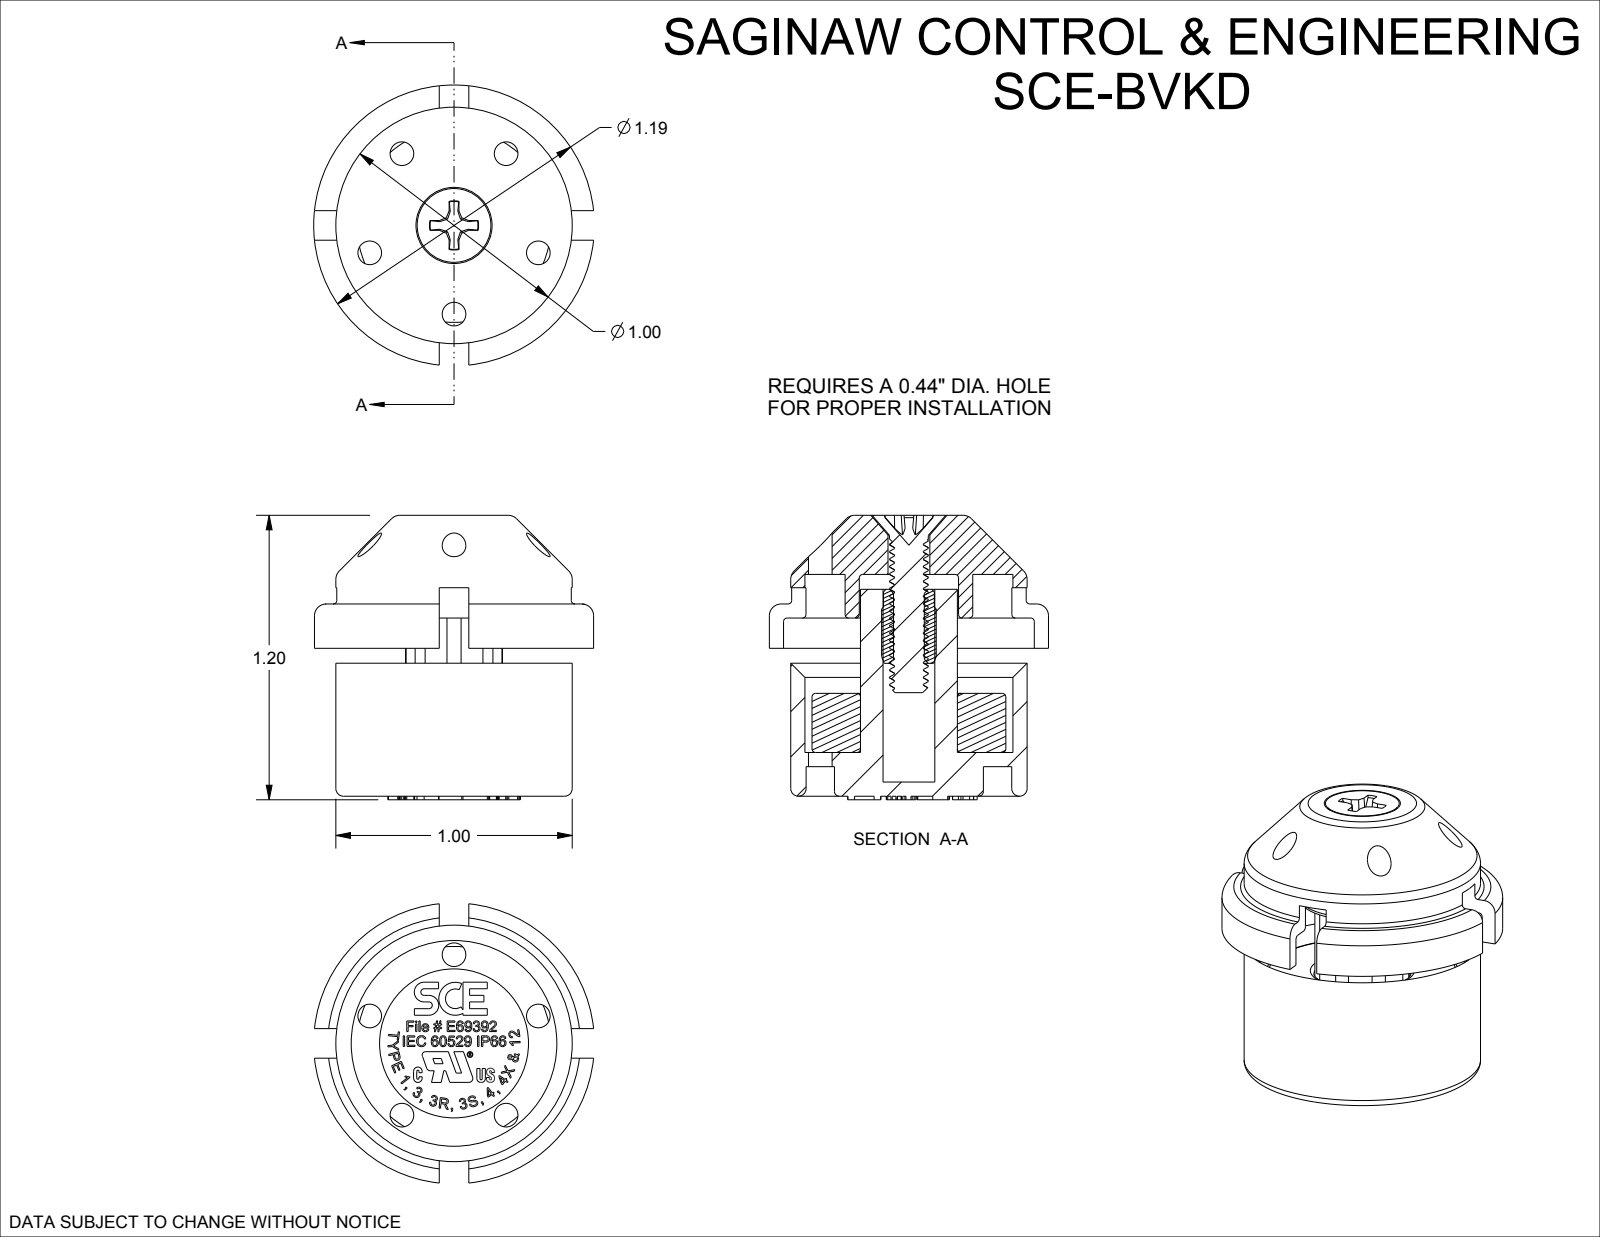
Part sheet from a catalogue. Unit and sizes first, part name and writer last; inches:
Units: inches
Overall size (bounding box): 1.188 × 1.181 × 1.181
Round holes (diameter × count): ⌀0.1 ×5, ⌀0.13 ×1, ⌀0.177 ×1, ⌀0.219 ×1, ⌀0.42 ×1, ⌀0.87 ×1, ⌀0.88 ×1, ⌀1.068 ×1
Round bosses / shafts (diameter × count): ⌀1.187 ×1, ⌀1 ×1, ⌀0.82 ×1, ⌀0.63 ×1, ⌀0.54 ×1, ⌀0.41 ×1, ⌀0.231 ×1, ⌀0.215 ×1
Partial cylindrical surfaces — rounded edges, fillets, slot ends (radius × count): R0.146 ×8
Main face-to-face distances: 0.753, 0.25, 0.503, 0.125, 0.06, 0.628, 0.185, 0.435, 0.938, 0.31
Hole centre spacings: 0.375, 0.441, 0.713, 0.714
Volume: 0.522 in³ · Surface area: 13.96 in²
Bodies: 5 solids, 199 faces (62 planar, 68 cylindrical, 69 other)
Part name (STEP PRODUCT): SCE-BVKD
STEP written by: SolidWorks 2021 (AUTOMOTIVE_DESIGN)
